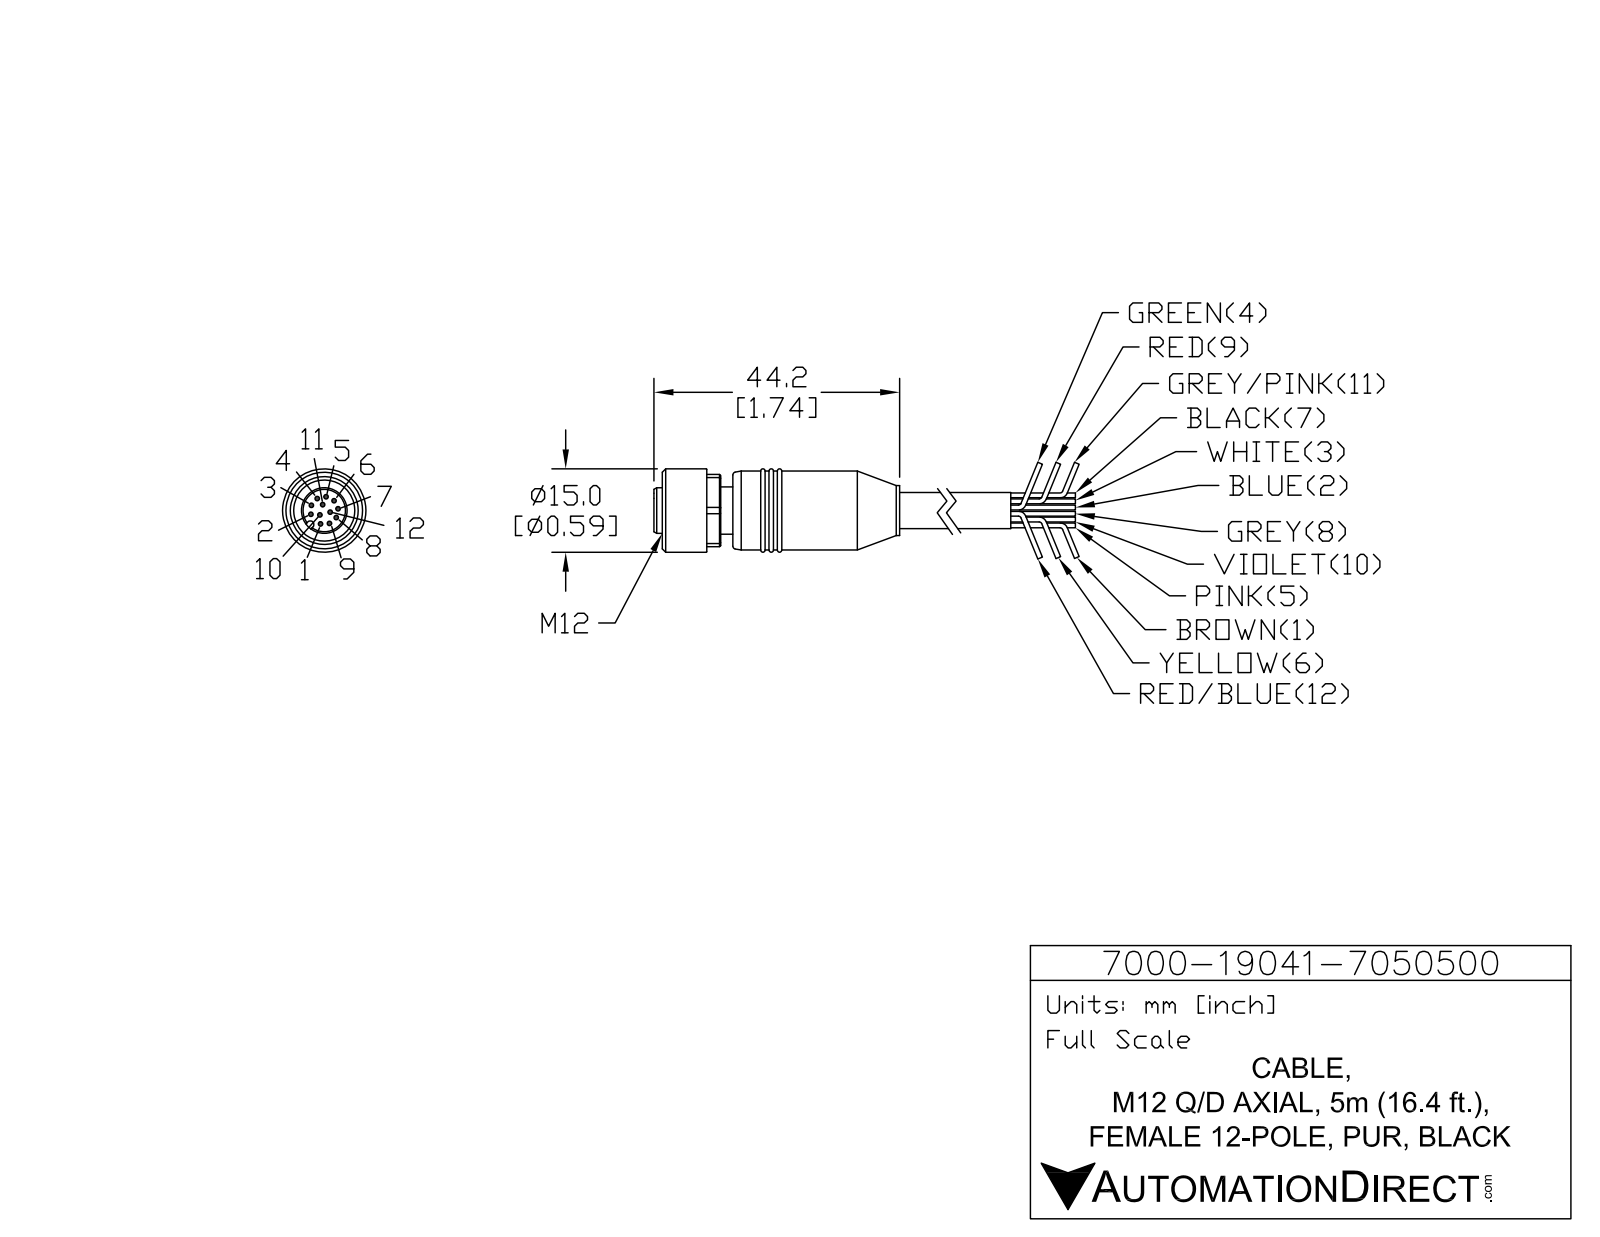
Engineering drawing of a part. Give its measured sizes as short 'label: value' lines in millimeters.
name: 7000-19041-7050500
written by: SolidWorks 2015 (AUTOMOTIVE_DESIGN)
unit: mm
bodies: 1 solid, 115 faces (35 planar, 52 cylindrical, 28 other)
size: 64.2 × 15 × 15
volume: 6 619 mm³; area: 3 428 mm²
holes: 12× ⌀0.8, 1× ⌀11
bosses: 1× ⌀15, 1× ⌀14.2, 1× ⌀9, 1× ⌀8.5, 1× ⌀8.2, 1× ⌀6.5
rounds: 1× R0.65, 1× R7.2
face distances: 2.2, 13, 3, 5.2, 9, 12, 14.2, 64.2, 55.2, 52.2
hole spacings: 2.5, 1.61, 4.17, 3.05, 4.84, 4.99, 1.1, 4.61
